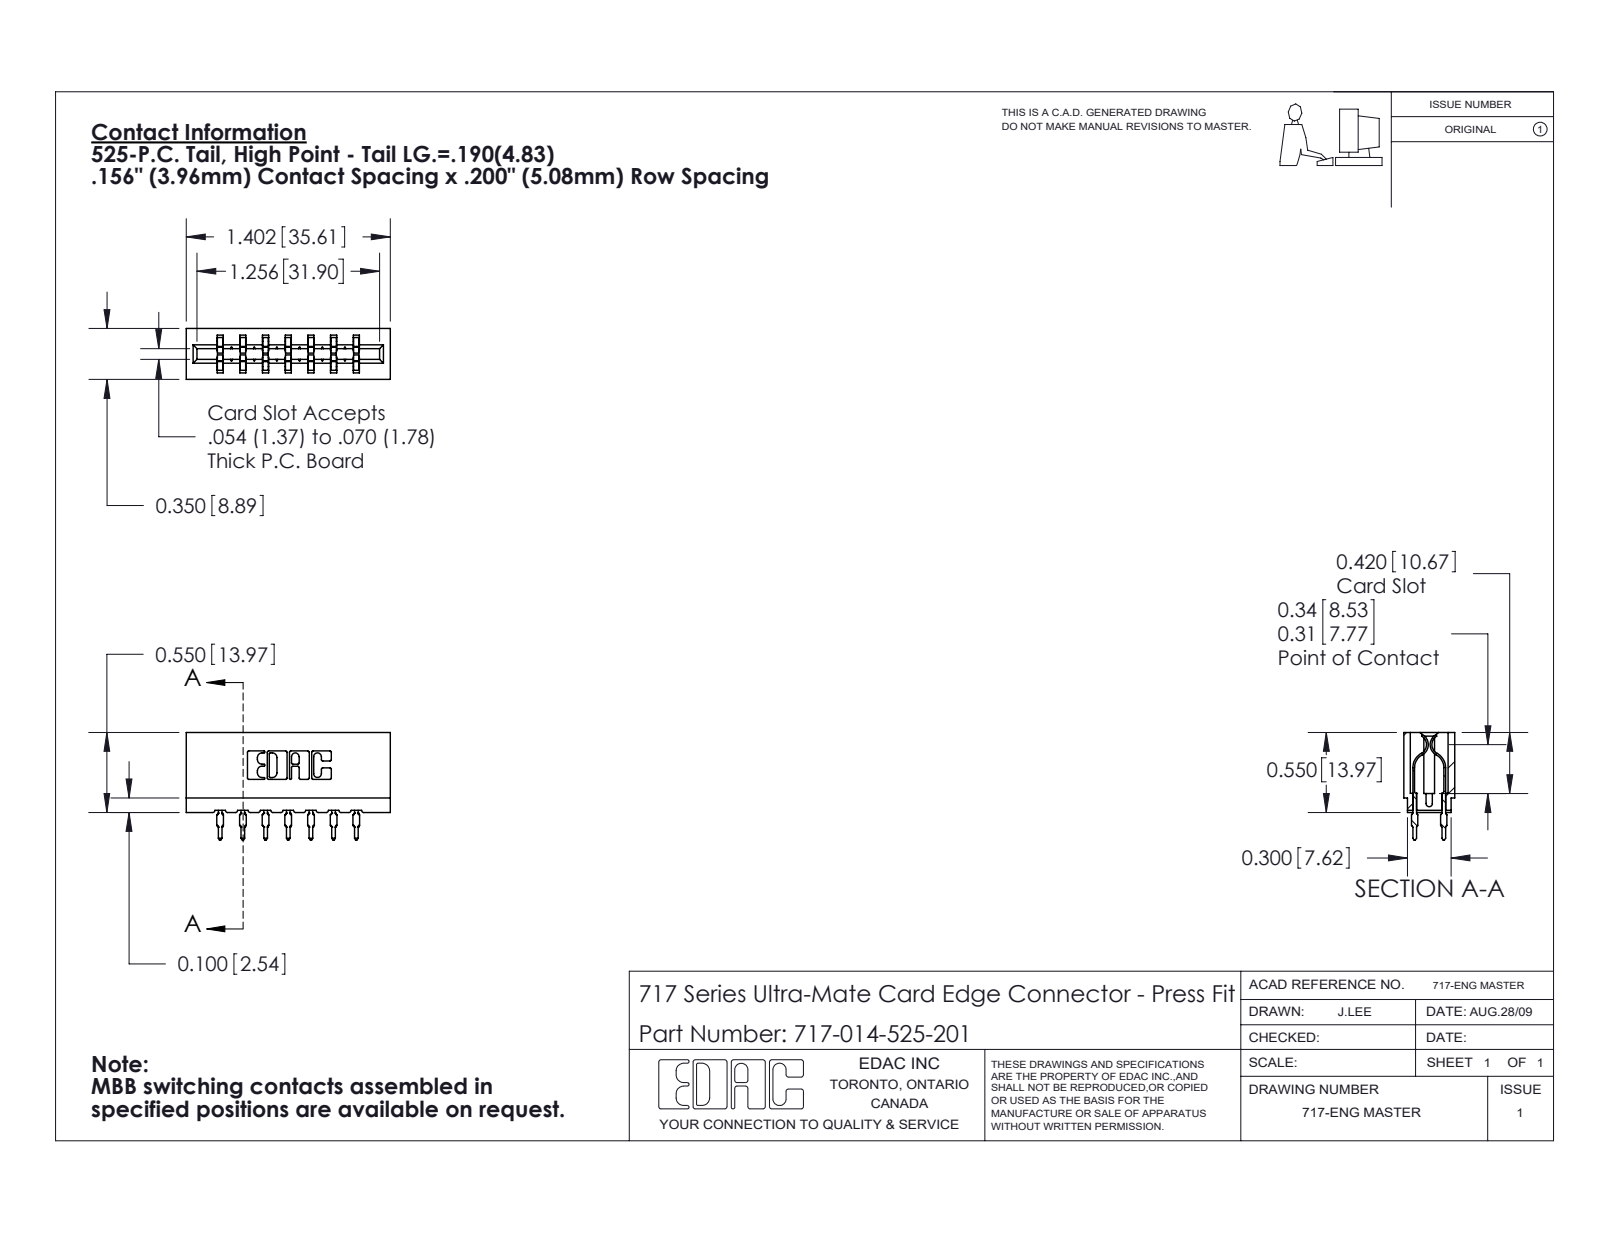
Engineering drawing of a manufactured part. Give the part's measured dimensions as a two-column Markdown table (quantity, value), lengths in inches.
| quantity | value |
| --- | --- |
| part name | 717-014-525-201; 717 Part_Insulator Option - 06; 745-292-001_525 |
| STEP written by | SolidWorks 2020 (CONFIG_CONTROL_DESIGN) |
| units | inches |
| bodies | 15 solids, 1354 faces (705 planar, 285 cylindrical, 364 other) |
| overall size | 1.402 × 0.739 × 0.35 |
| volume | 0.197 in³ |
| surface area | 6.898 in² |
| partial cylindrical surfaces (radius × count) | 0.021 × 28, 0.01 × 22, 0.015 × 14, 0.005 × 8, 0.011 × 8, 0.007 × 6, 0.031 × 6, 0.026 × 3 |
| main face-to-face distances | 0.212, 0.156, 0.138, 0.624, 0.35, 0.198, 0.312, 0.468, 0.042, 0.27 |
